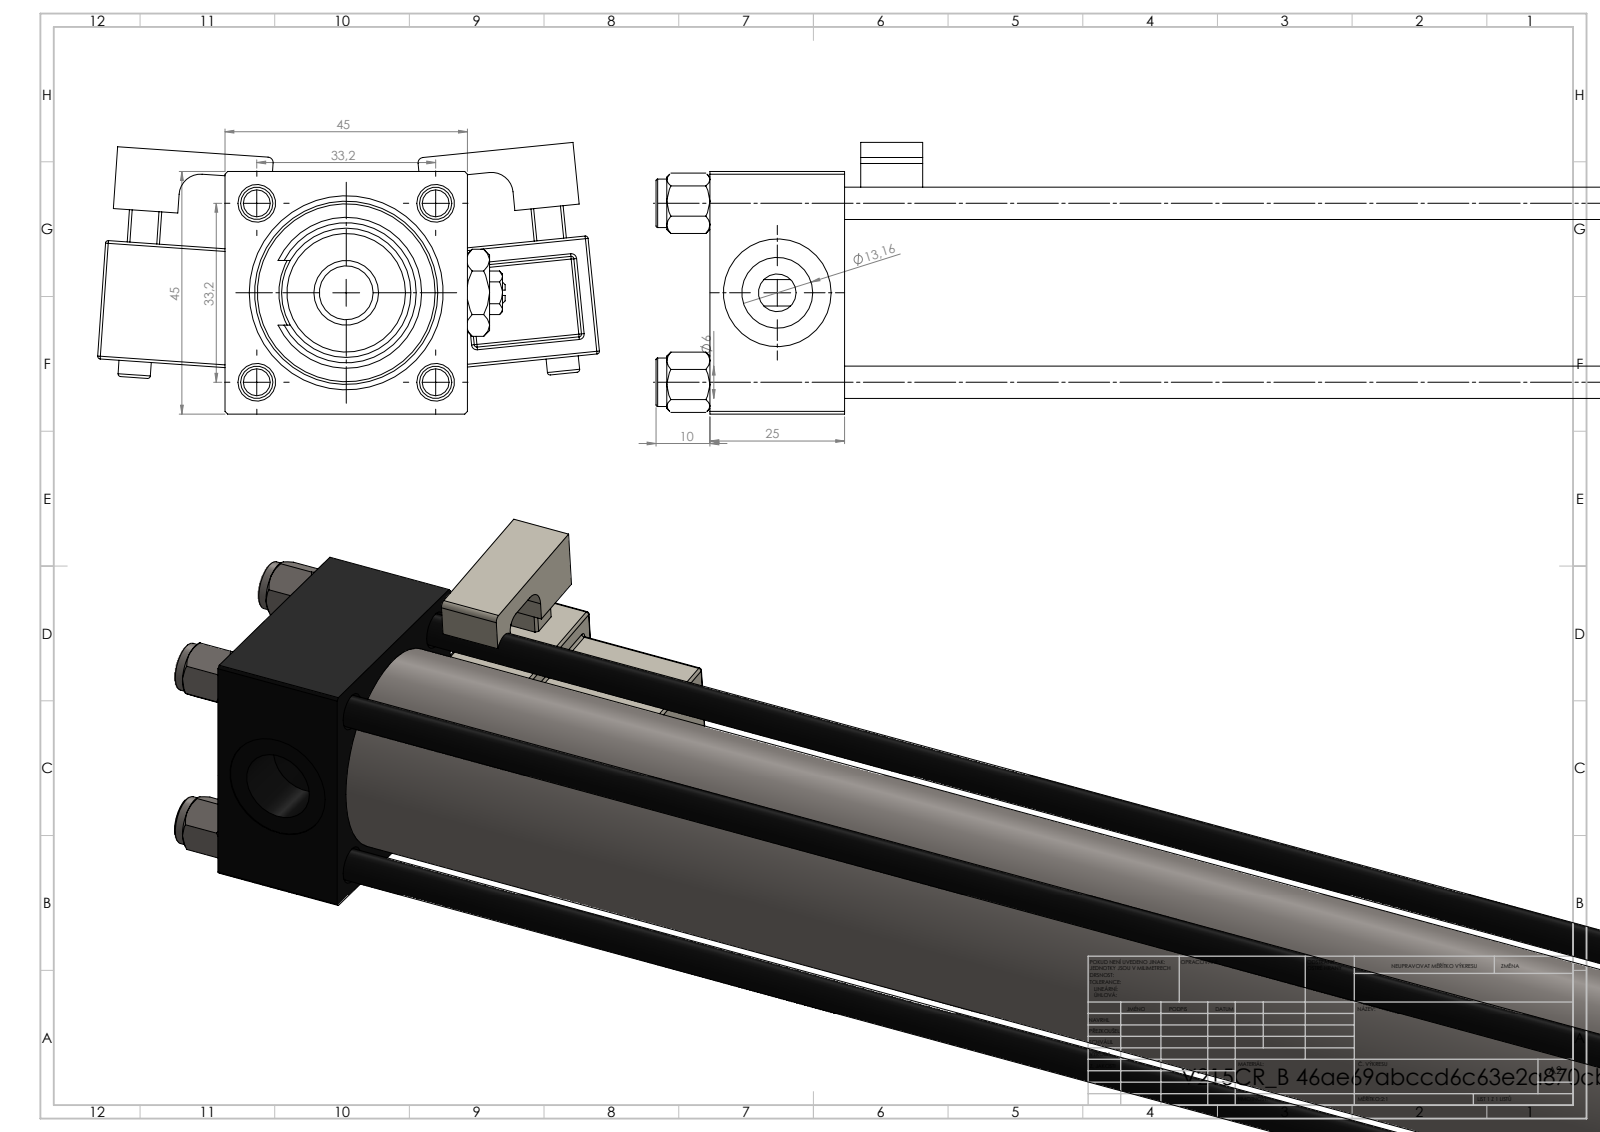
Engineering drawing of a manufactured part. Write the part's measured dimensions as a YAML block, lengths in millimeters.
part_name: "V215CR_B-1; Zatka_pro_OIL_PORT; NUT_M5_B; MFA (+5 more)"
step_written_by: "SolidWorks 2019 (CONFIG_CONTROL_DESIGN)"
units: millimeters
bodies: {solids: 17, faces: 1499, planar: 568, cylindrical: 161, other: 770}
overall_size: [499, 93.14, 50.4]
volume: 501785
surface_area: 199790
round_holes:
  - {diameter: 6, count: 4}
  - {diameter: 7, count: 2}
  - {diameter: 13.16, count: 2}
  - {diameter: 20, count: 2}
  - {diameter: 10.5, count: 1}
  - {diameter: 22, count: 1}
  - {diameter: 24, count: 1}
  - {diameter: 25, count: 1}
  - {diameter: 32, count: 1}
  - {diameter: 33, count: 1}
round_bosses_or_shafts:
  - {diameter: 9, count: 4}
  - {diameter: 6, count: 2}
  - {diameter: 38, count: 1}
  - {diameter: 34, count: 1}
  - {diameter: 28, count: 1}
  - {diameter: 18, count: 1}
  - {diameter: 12, count: 1}
  - {diameter: 11, count: 1}
partial_cylinders:
  - {radius: 0.5, count: 48}
  - {radius: 1, count: 2}
  - {radius: 2.5, count: 2}
  - {radius: 4, count: 2}
  - {radius: 9.75, count: 1}
  - {radius: 10.5, count: 1}
face_to_face_distances: [45, 25, 355, 330, 3, 403, 14.5, 15, 312.5, 17.5]
hole_center_spacings: [23.48, 33.2, 46.95, 355.5]
